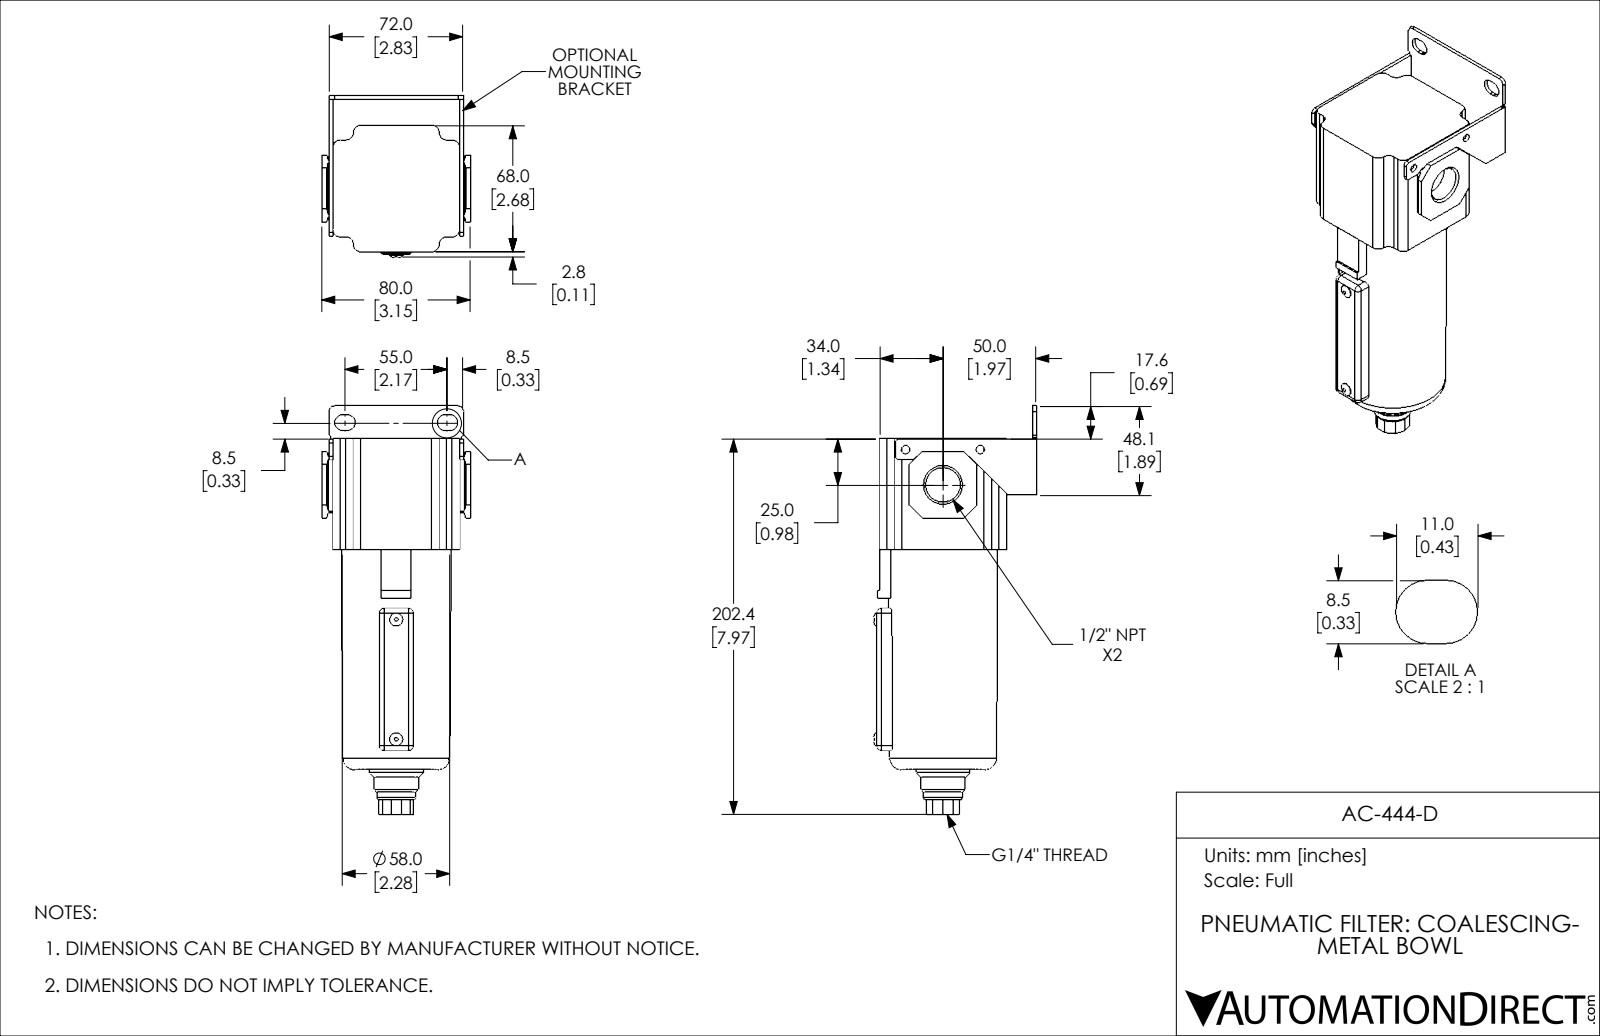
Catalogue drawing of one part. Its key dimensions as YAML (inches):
part_name: "AC-444-D"
step_written_by: "SolidWorks 2018 (AUTOMOTIVE_DESIGN)"
units: inches
bodies: {solids: 1, faces: 193, planar: 109, cylindrical: 60, other: 24}
overall_size: [8.661, 3.417, 3.15]
volume: 36.4
surface_area: 96.11
round_holes:
  - {diameter: 0.177, count: 2}
  - {diameter: 0.451, count: 1}
  - {diameter: 0.734, count: 1}
round_bosses_or_shafts:
  - {diameter: 0.276, count: 2}
  - {diameter: 1.102, count: 1}
  - {diameter: 0.906, count: 1}
  - {diameter: 0.787, count: 1}
partial_cylinders:
  - {radius: 0.157, count: 12}
  - {radius: 0.098, count: 8}
  - {radius: 0.167, count: 4}
  - {radius: 0.079, count: 3}
  - {radius: 0.039, count: 2}
  - {radius: 0.118, count: 2}
face_to_face_distances: [0.079, 2.677, 2.756, 0.63, 2.362, 3.228, 3.307, 0.551, 0.157, 0.236]
hole_center_spacings: [1.086, 1.575]
